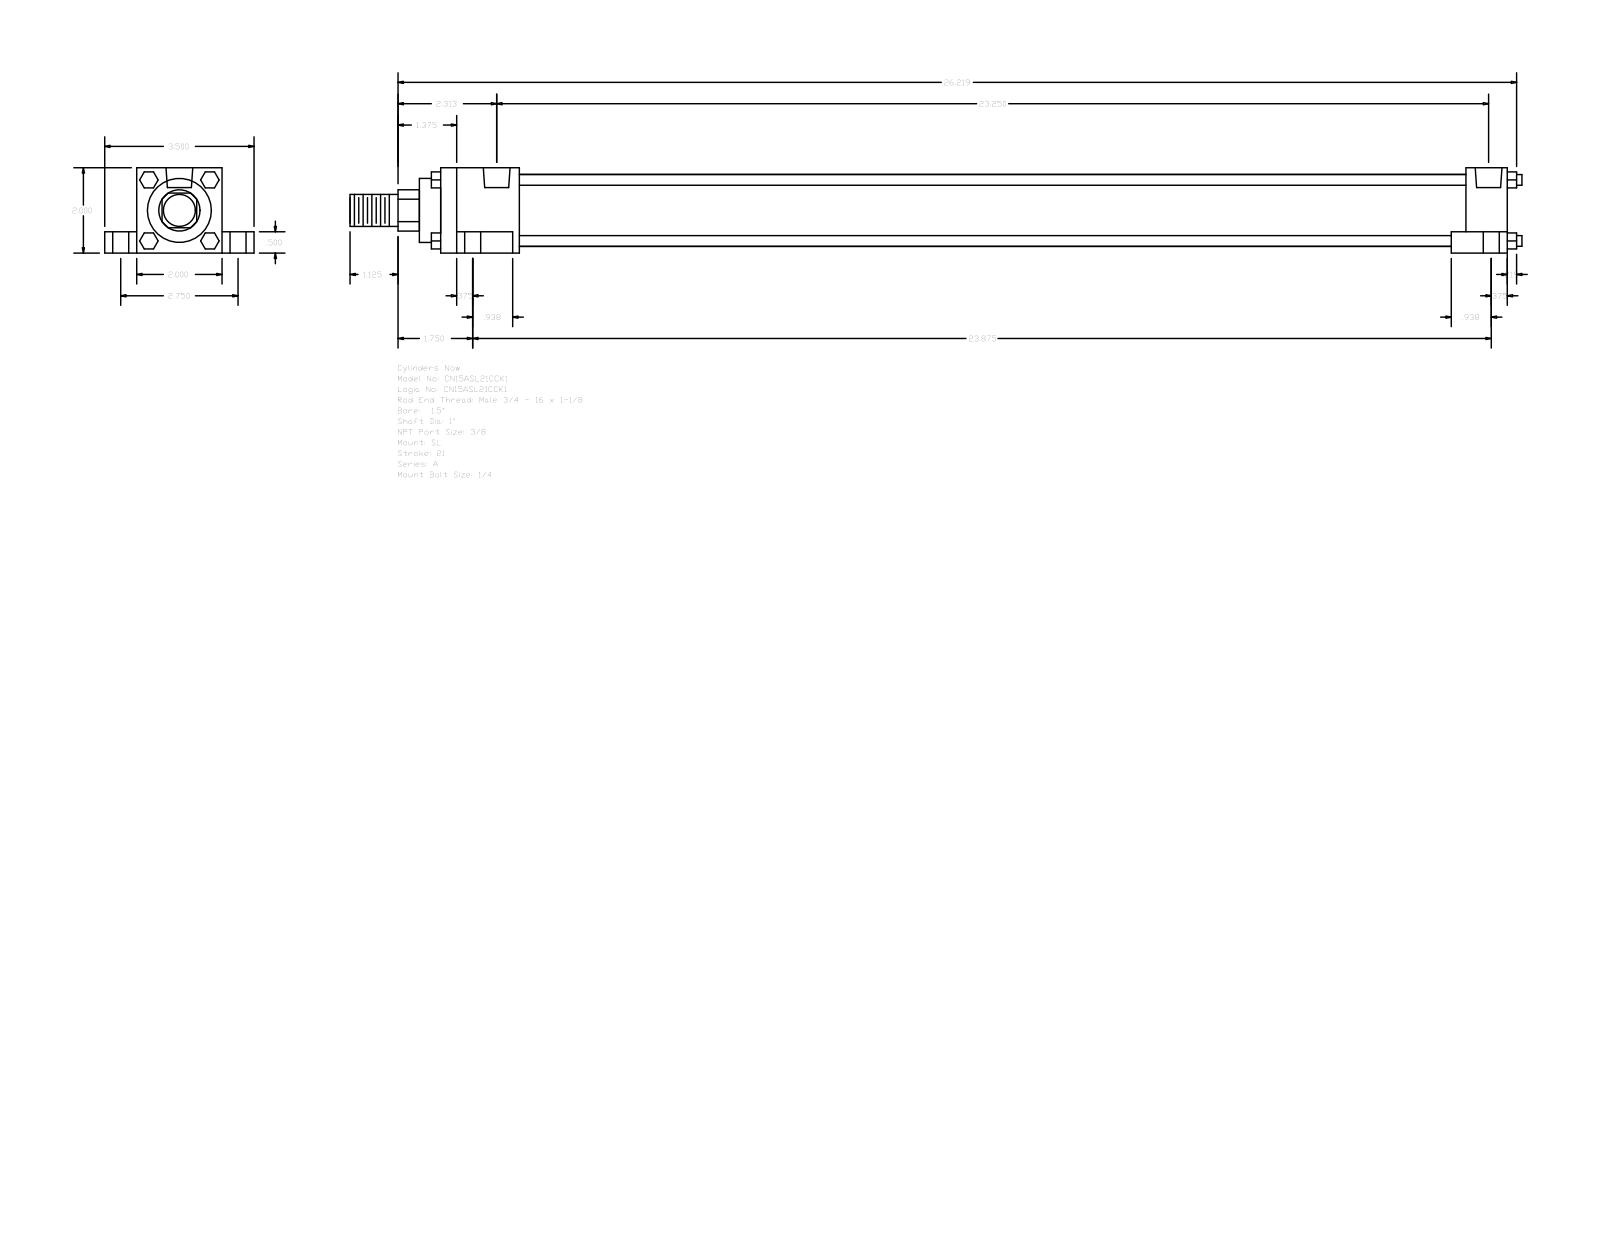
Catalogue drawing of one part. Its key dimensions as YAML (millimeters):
part_name: "A_SL__0150_1"
step_written_by: "GSSL Pune (CONFIG_CONTROL_DESIGN)"
units: millimeters
bodies: {solids: 0, faces: 148, planar: 112, cylindrical: 36, other: 0}
overall_size: [697.71, 88.9, 50.8]
round_holes:
  - {diameter: 5.56, count: 4}
  - {diameter: 9.53, count: 4}
  - {diameter: 15.88, count: 4}
  - {diameter: 15.93, count: 2}
round_bosses_or_shafts:
  - {diameter: 6.35, count: 4}
  - {diameter: 42.93, count: 1}
  - {diameter: 38.1, count: 1}
  - {diameter: 25.4, count: 1}
  - {diameter: 19.05, count: 1}
partial_cylinders:
  - {radius: 12.29, count: 1}
face_to_face_distances: [50.8, 12.7, 38.1, 19.05, 69.85, 9.52, 635, 33.34, 610.39, 24.61]
hole_center_spacings: [3.97, 34.96, 35.36, 37.73, 39.41, 69.84, 582.61, 586.58]
